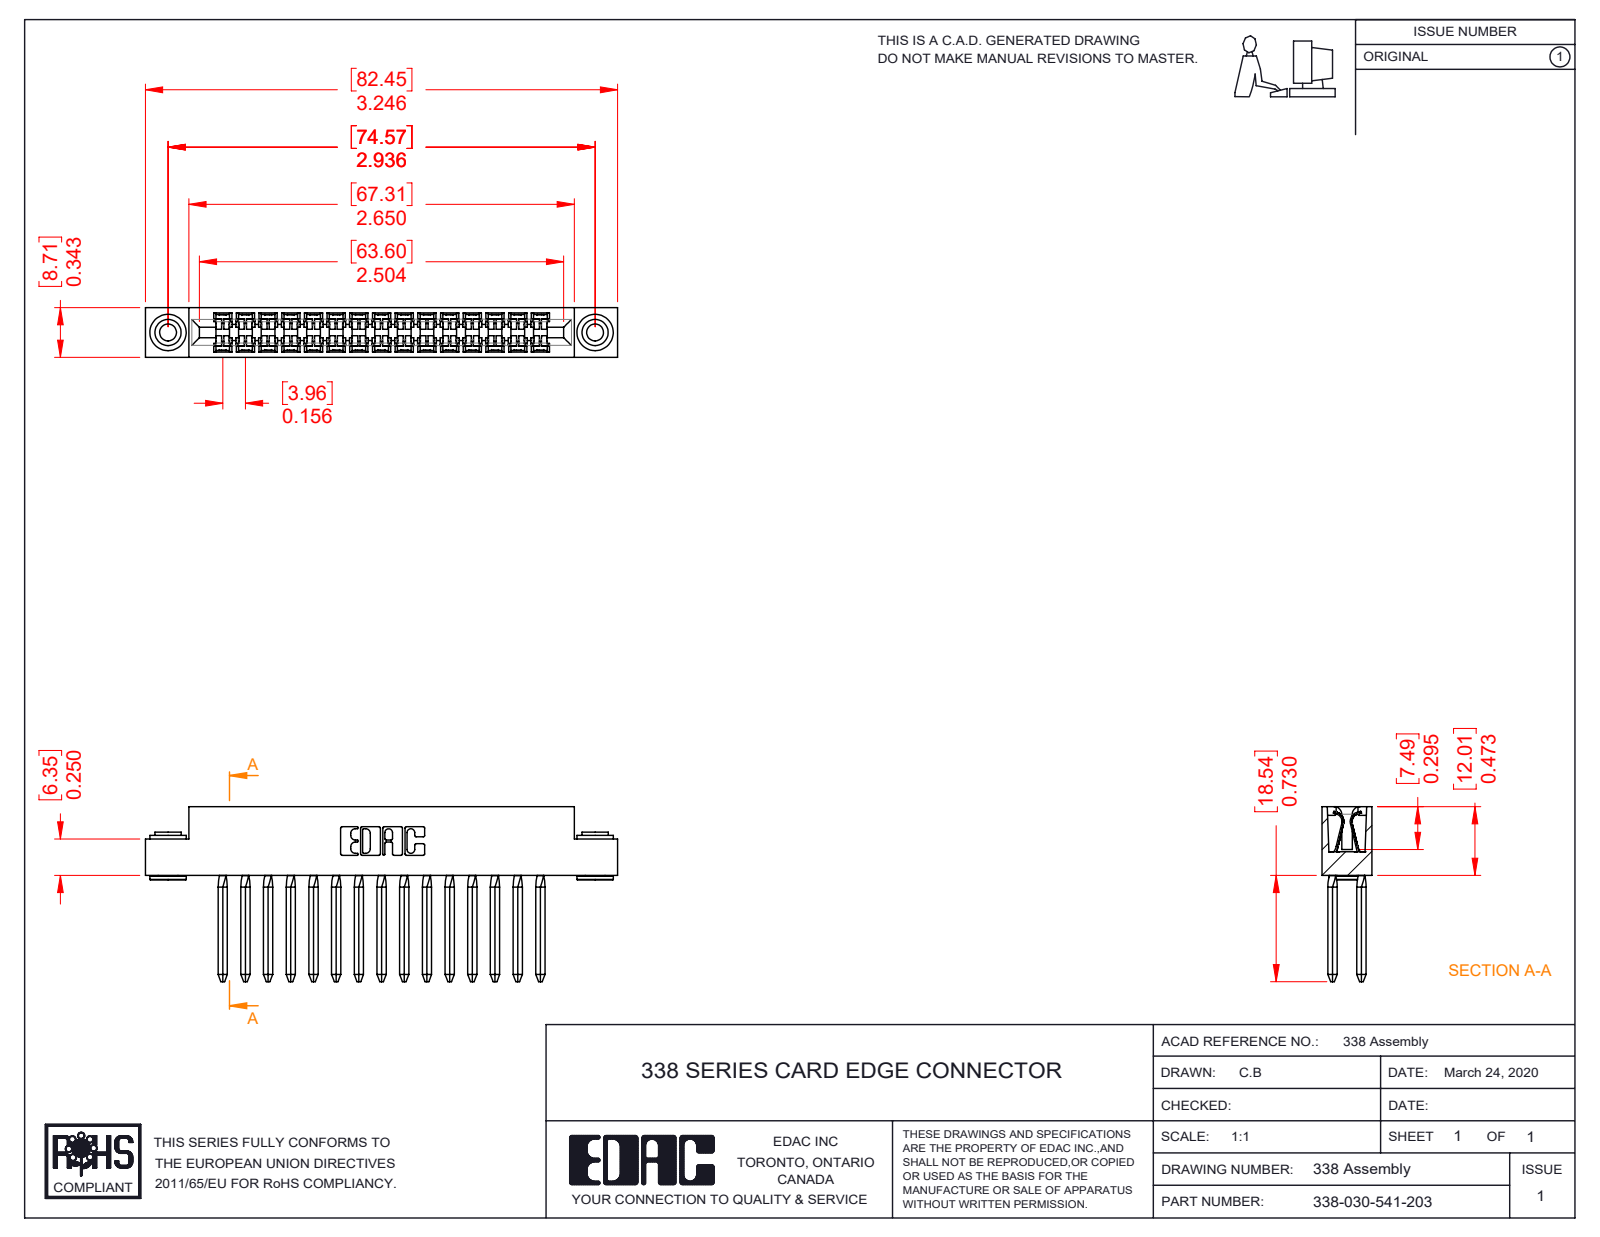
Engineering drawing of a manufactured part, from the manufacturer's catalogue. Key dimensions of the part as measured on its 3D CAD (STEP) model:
Part name (STEP PRODUCT): 338-210-001_338-210-015-004; 338-290-001_541; 338-030-541-203; 345-250-002_345-250-002-102
STEP written by: SolidWorks 2016 (CONFIG_CONTROL_DESIGN)
Units: inches
Bodies: 33 solids, 2156 faces (1484 planar, 544 cylindrical, 128 other)
Overall size (bounding box): 3.246 × 1.203 × 0.343
Volume: 0.382 in³ · Surface area: 17.67 in²
Round holes (diameter × count): ⌀0.116 ×2, ⌀0.156 ×2
Round bosses / shafts (diameter × count): ⌀0.25 ×2, ⌀0.18 ×2, ⌀0.136 ×2
Partial cylindrical surfaces — rounded edges, fillets, slot ends (radius × count): R0.025 ×92, R0.008 ×30, R0.055 ×24, R0.067 ×24, R0.1 ×24, R0.01 ×22, R0.007 ×6, R0.031 ×6
Main face-to-face distances: 0.343, 0.156, 0.11, 0.624, 0.468, 0.221, 0.78, 0.135, 0.207, 0.25
Hole centre spacings: 2.936
